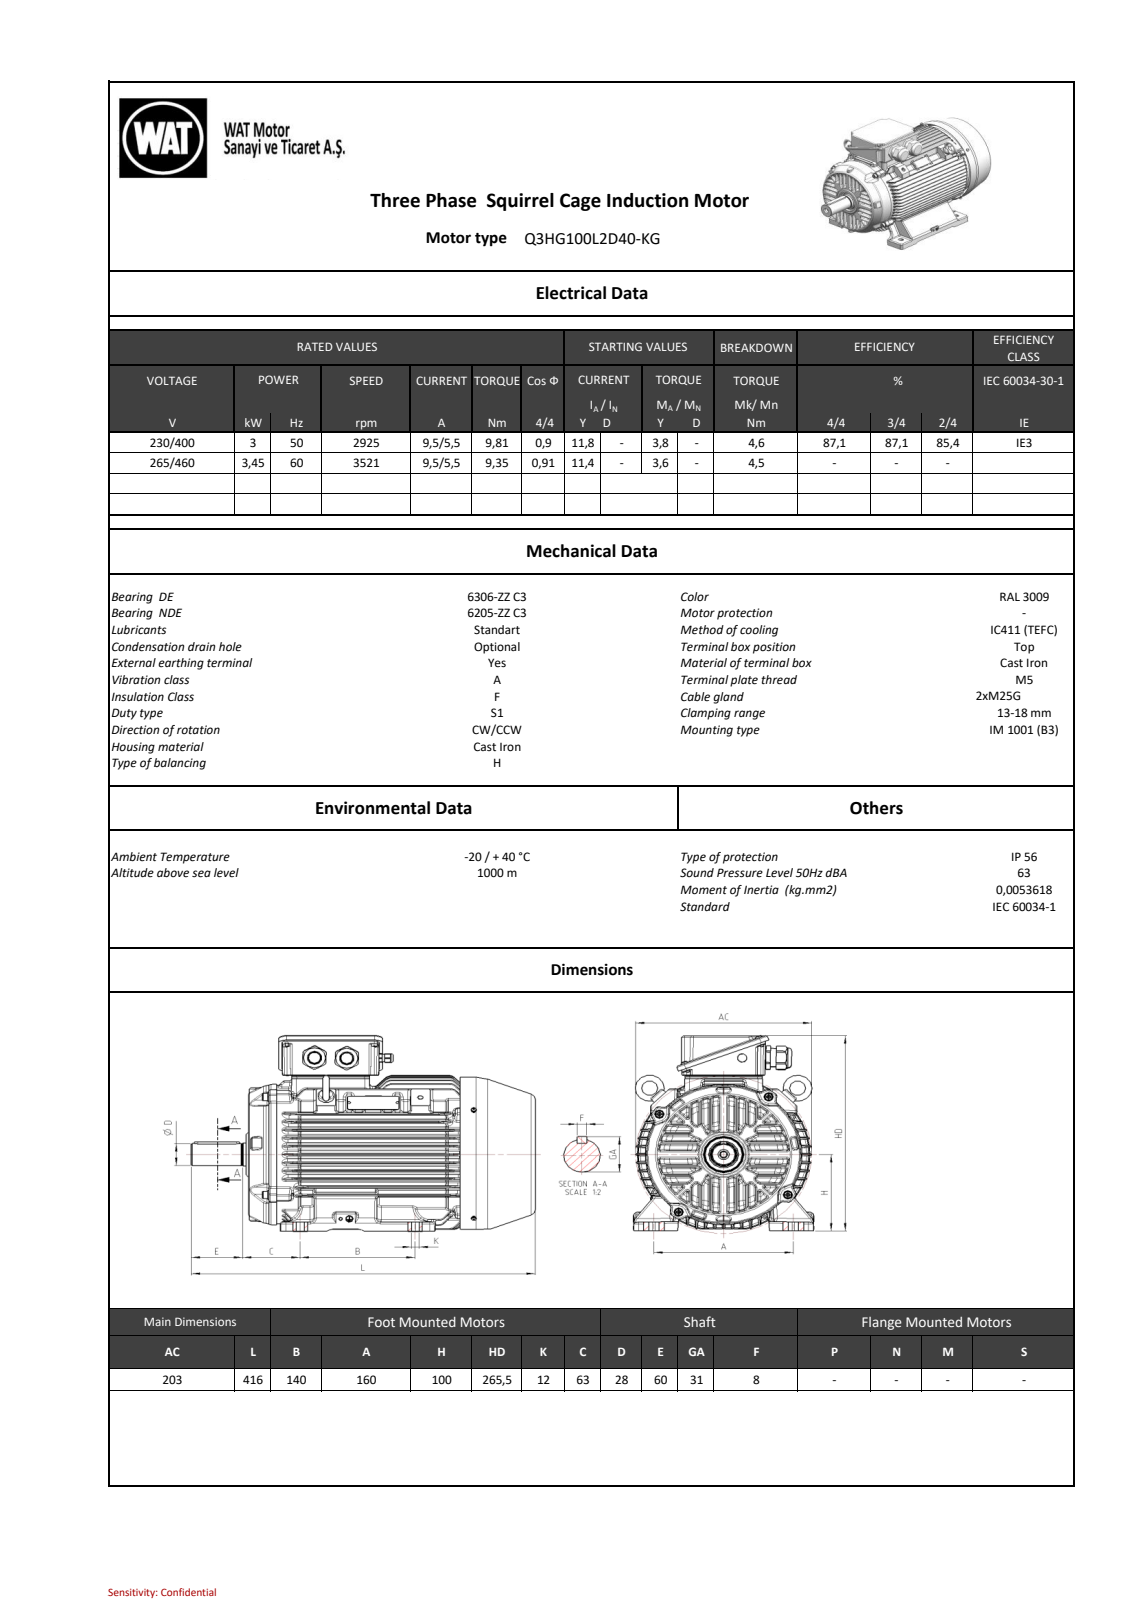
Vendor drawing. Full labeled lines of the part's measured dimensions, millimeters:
Part name (STEP PRODUCT): C901A24426BAzdo7
STEP written by: SIEMENS PLM Software NX 11.0 (AUTOMOTIVE_DESIGN)
Units: millimetres
Bodies: 0 solids, 4919 faces (928 planar, 1316 cylindrical, 2675 other)
Overall size (bounding box): 416 × 265.48 × 204.29
Round holes (diameter × count): ⌀5 ×8, ⌀10 ×3, ⌀6.8 ×2, ⌀17.2 ×2, ⌀4.2 ×1, ⌀6.5 ×1, ⌀8.5 ×1, ⌀10.5 ×1, ⌀43.4 ×1, ⌀43.6 ×1, ⌀197 ×1
Round bosses / shafts (diameter × count): ⌀10 ×8, ⌀12 ×4, ⌀8.65 ×4, ⌀8 ×4, ⌀4 ×4, ⌀27.7 ×2, ⌀25.25 ×2, ⌀20 ×2
Partial cylindrical surfaces — rounded edges, fillets, slot ends (radius × count): R3 ×375, R1.5 ×110, R2 ×75, R1.8 ×48, R1 ×38, R0.25 ×28, R5 ×18, R26.5 ×12
Main face-to-face distances: 13.52, 13.61, 27.13, 78.72, 51.59, 65.11, 40.83, 27.31, 13.7, 37.89
Hole centre spacings: 89.5, 126.57, 31.07, 102.68, 146.62, 176.28, 179, 44.5
